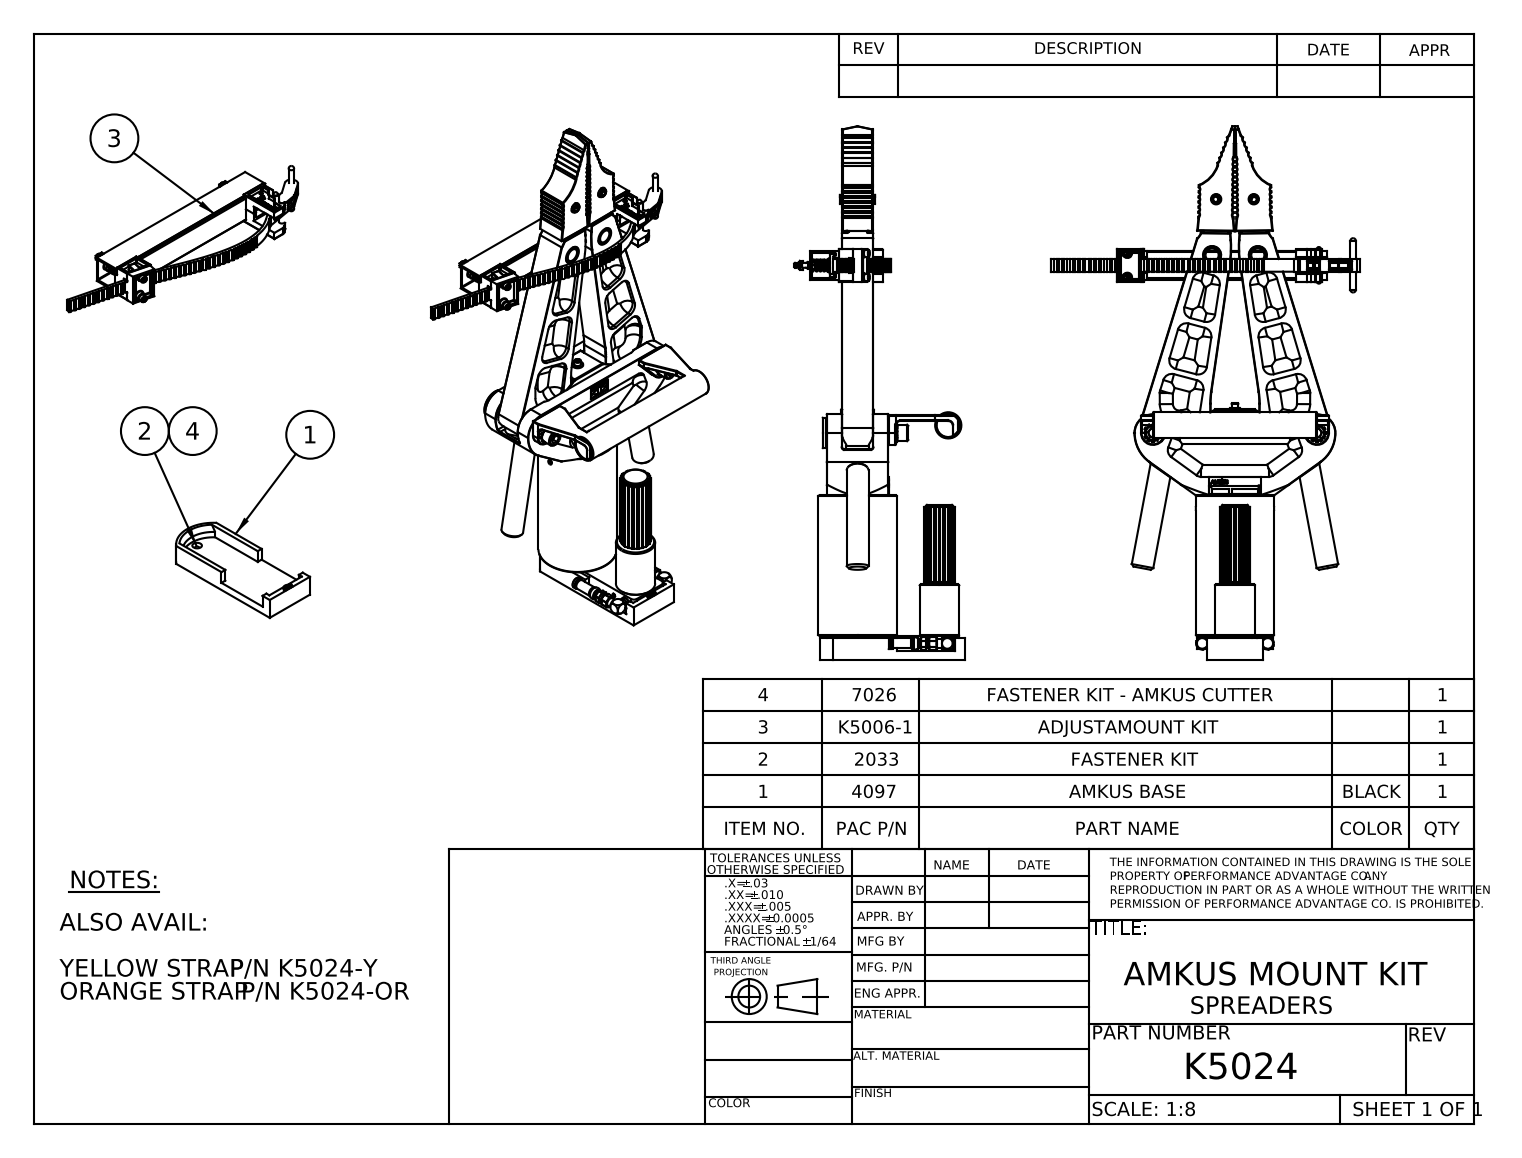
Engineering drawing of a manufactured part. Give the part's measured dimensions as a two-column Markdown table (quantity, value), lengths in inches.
| quantity | value |
| --- | --- |
| part name | .25-20 x 1.0 lg Hex Bolt_HBOLT 0.2500-20x1x1-N; 2035 Pack_10" apart; 2002_HX-SHCS 0.25-20x0.75x0.75-N; 2011 (+8 more) |
| STEP written by | SolidWorks 2010 (CONFIG_CONTROL_DESIGN) |
| units | inches |
| bodies | 23 solids, 2763 faces (978 planar, 970 cylindrical, 815 other) |
| overall size | 30.518 × 14.173 × 8.961 |
| volume | 43.66 in³ |
| surface area | 1 516 in² |
| round holes (diameter × count) | 0.406 × 8, 0.201 × 6, 0.25 × 4, 1 × 4, 0.266 × 3, 0.19 × 2, 0.269 × 2, 0.288 × 2, 0.313 × 2, 0.531 × 2, 0.75 × 2, 0.109 × 1 |
| round bosses / shafts (diameter × count) | 0.375 × 5, 0.25 × 5, 0.625 × 3, 1.75 × 2, 1.5 × 2, 1.25 × 2, 0.937 × 2, 0.635 × 2 |
| partial cylindrical surfaces (radius × count) | 0.03 × 100, 0.5 × 82, 0.062 × 66, 0.031 × 45, 0.125 × 43, 0.063 × 40, 0.032 × 35, 0.02 × 30 |
| main face-to-face distances | 1.772, 0.822, 0.854, 2.646, 2.678, 0.032, 1.823, 2.636, 0.864, 0.188 |
| hole center spacings | 1.225, 1.948, 0.604, 0.798, 1.043, 1.641, 1.722, 2.517 |
